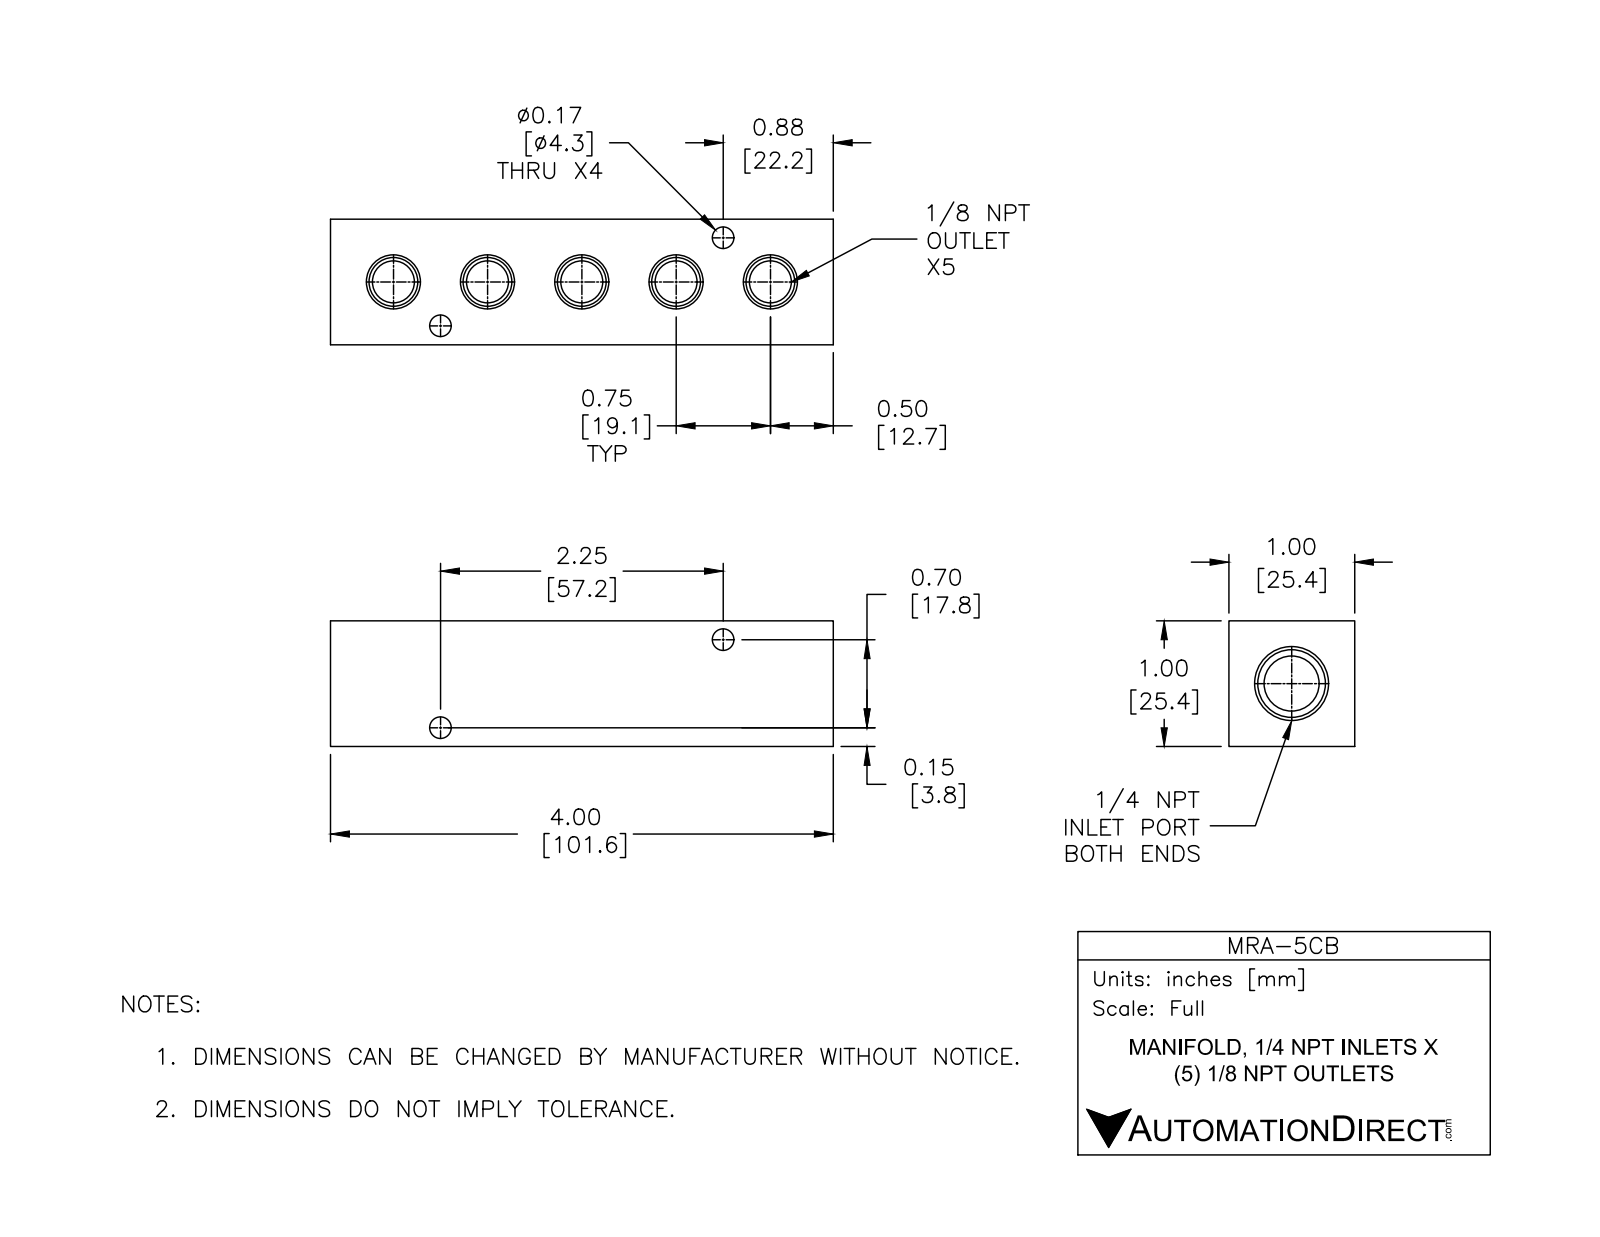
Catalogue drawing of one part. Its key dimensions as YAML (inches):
part_name: "MRA-5CB"
step_written_by: "SolidWorks 2015 (CONFIG_CONTROL_DESIGN)"
units: inches
bodies: {solids: 1, faces: 68, planar: 13, cylindrical: 27, other: 28}
overall_size: [4, 1, 1]
volume: 3.079
surface_area: 25.92
round_holes:
  - {diameter: 0.17, count: 4}
  - {diameter: 0.332, count: 3}
  - {diameter: 0.438, count: 1}
partial_cylinders:
  - {radius: 0.166, count: 2}
face_to_face_distances: [1, 4, 0.73, 0.27, 0.39, 3.61, 3.22]
hole_center_spacings: [0.513, 0.75, 2.356, 1.178, 1.178, 1.5, 1.907, 1.907]
